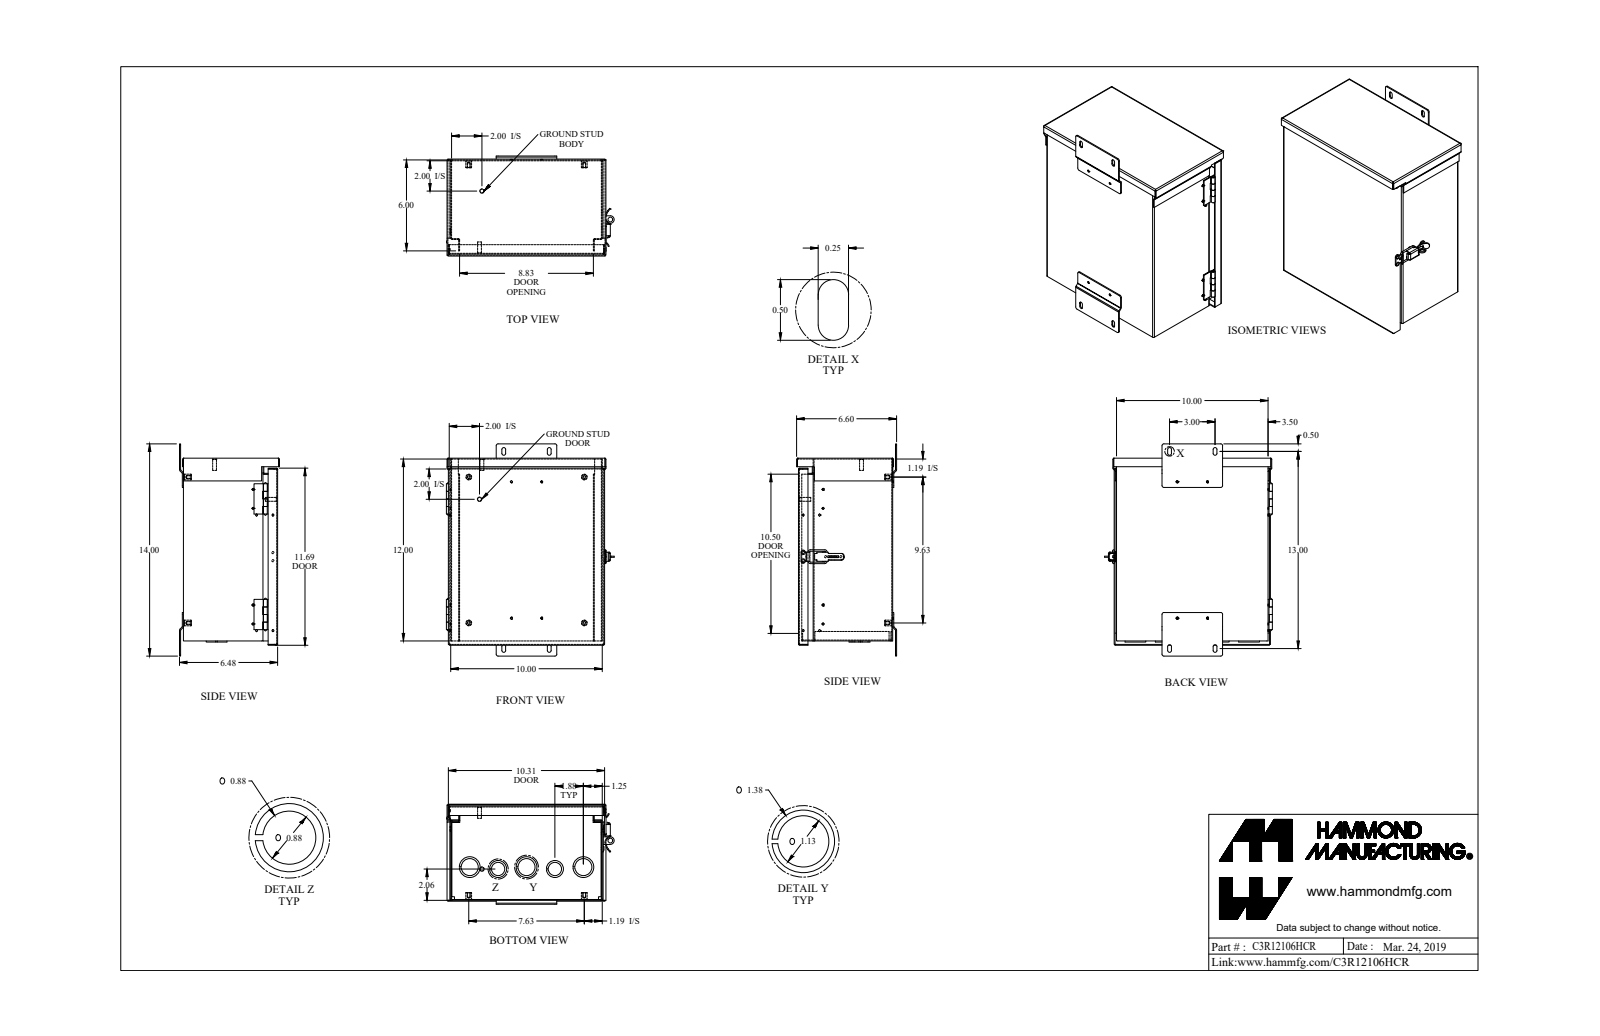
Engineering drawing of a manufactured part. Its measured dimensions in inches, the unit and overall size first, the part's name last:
Units: inches
Overall size (bounding box): 14 × 11.07 × 6.599
Round holes (diameter × count): ⌀0.137 ×4, ⌀0.14 ×4, ⌀0.156 ×4, ⌀1.125 ×3, ⌀0.133 ×2, ⌀0.145 ×2, ⌀0.875 ×2, ⌀0.125 ×1, ⌀0.13 ×1, ⌀0.313 ×1
Round bosses / shafts (diameter × count): ⌀0.131 ×12, ⌀0.375 ×4, ⌀0.1 ×4, ⌀1.375 ×3, ⌀0.125 ×3, ⌀1.125 ×2, ⌀0.281 ×2, ⌀0.25 ×2
Partial cylindrical surfaces — rounded edges, fillets, slot ends (radius × count): R0.029 ×28, R0.086 ×28, R0.125 ×21, R0.036 ×6, R0.108 ×6, R0.135 ×2, R0.04 ×1, R0.068 ×1
Main face-to-face distances: 0.057, 6.16, 6.103, 9.943, 6.217, 12, 10, 0.187, 11.943, 9.886
Hole centre spacings: 1.498, 3.75, 1.01, 1.01, 1.879, 1.88, 2, 2.498
Volume: 43.04 in³ · Surface area: 1 386 in²
Bodies: 31 solids, 851 faces (499 planar, 297 cylindrical, 55 other)
Part name (STEP PRODUCT): C3R12106HCR_Default
STEP written by: SolidWorks 2019 (CONFIG_CONTROL_DESIGN)
